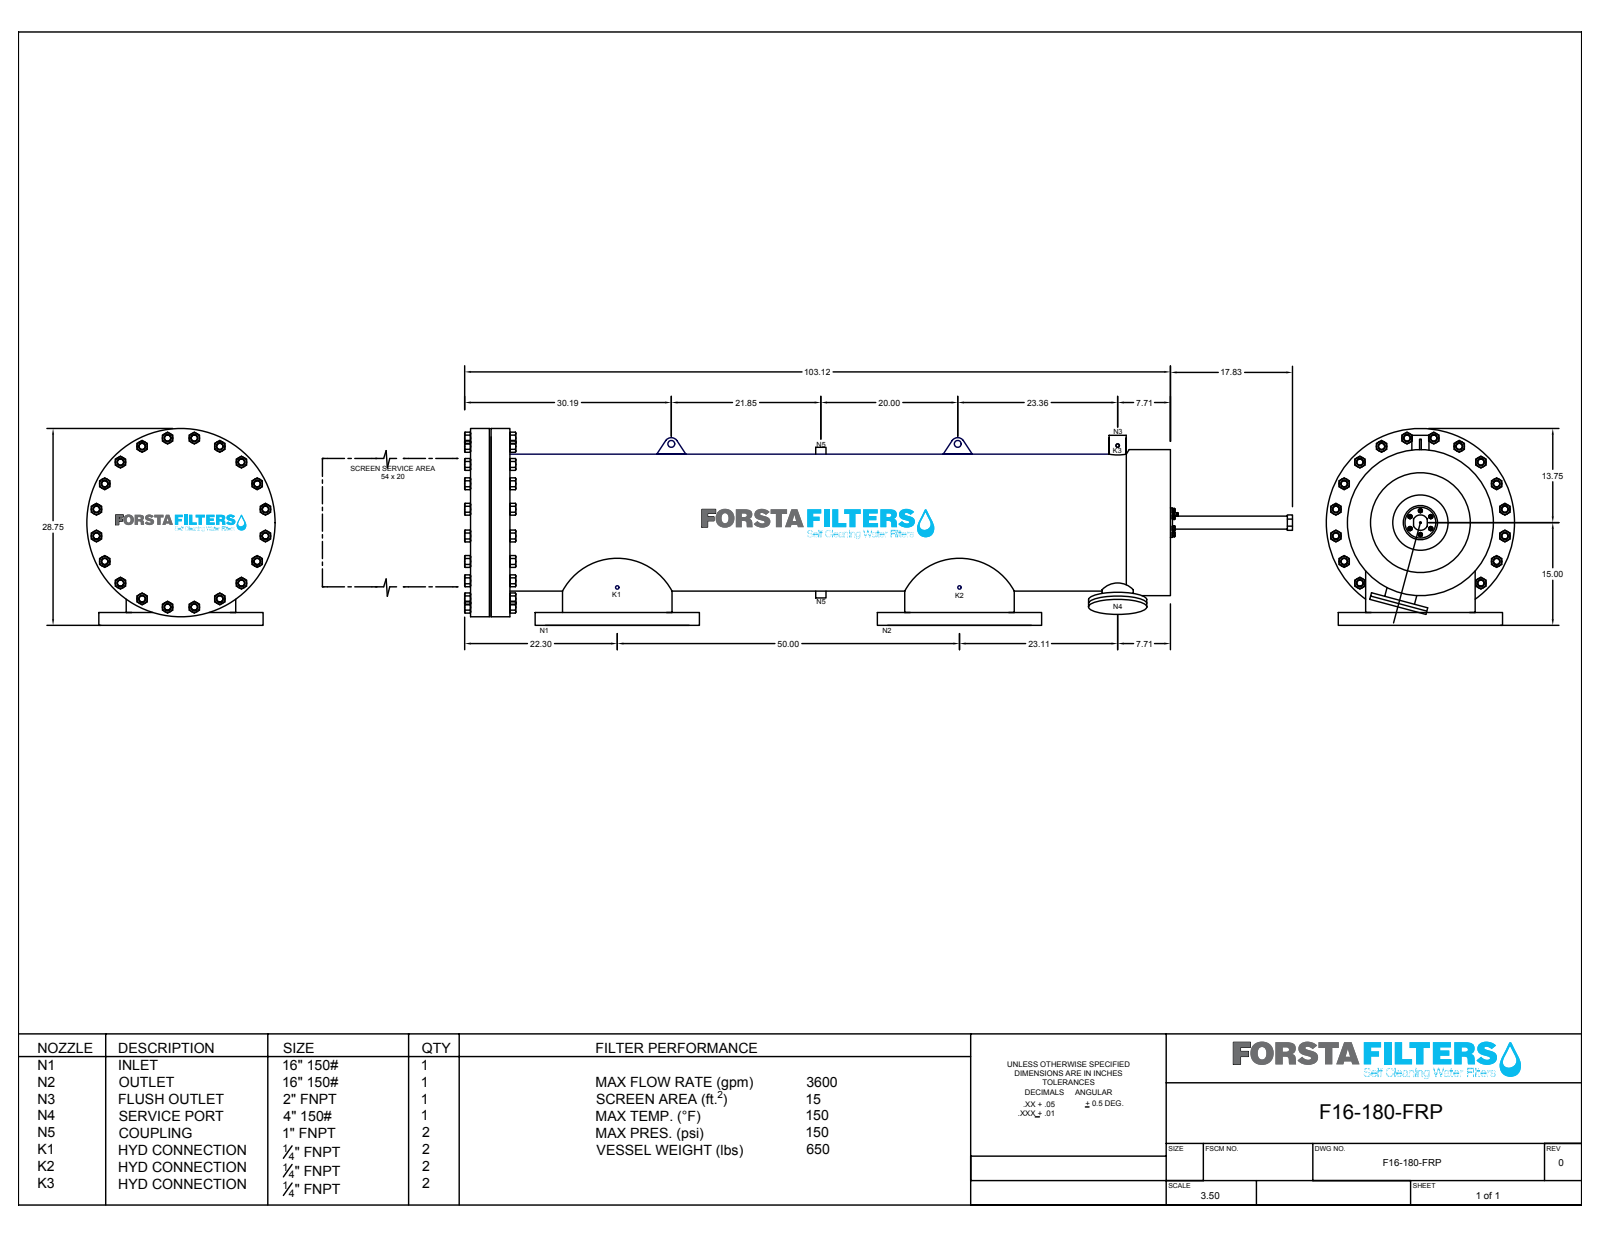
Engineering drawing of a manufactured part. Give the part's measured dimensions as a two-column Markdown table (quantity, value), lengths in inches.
| quantity | value |
| --- | --- |
| part name | F16-FRP-180 |
| STEP written by | SolidWorks 2018 (CONFIG_CONTROL_DESIGN) |
| units | inches |
| bodies | 23 solids, 808 faces (374 planar, 421 cylindrical, 13 other) |
| overall size | 116.454 × 30.749 × 27.498 |
| volume | 4 674 in³ |
| surface area | 19 477 in² |
| round holes (diameter × count) | 1.12 × 32, 1 × 19, 0.75 × 16, 0.38 × 6, 0.25 × 3, 4 × 2, 16 × 2, 0.246 × 1, 1.394 × 1, 2 × 1, 20.931 × 1 |
| round bosses / shafts (diameter × count) | 0.375 × 6, 23.5 × 2, 16.394 × 2, 9 × 2, 4.394 × 2, 0.644 × 2, 27.498 × 1, 21.325 × 1 |
| partial cylindrical surfaces (radius × count) | 1 × 2 |
| main face-to-face distances | 2.75, 3, 0.25, 1.44, 97.951, 95.201, 94.951, 97.754, 95.004, 94.754 |
| hole center spacings | 4.146, 20.842, 11.806, 8.132, 17.669, 5.303, 12.5, 17.678 |
